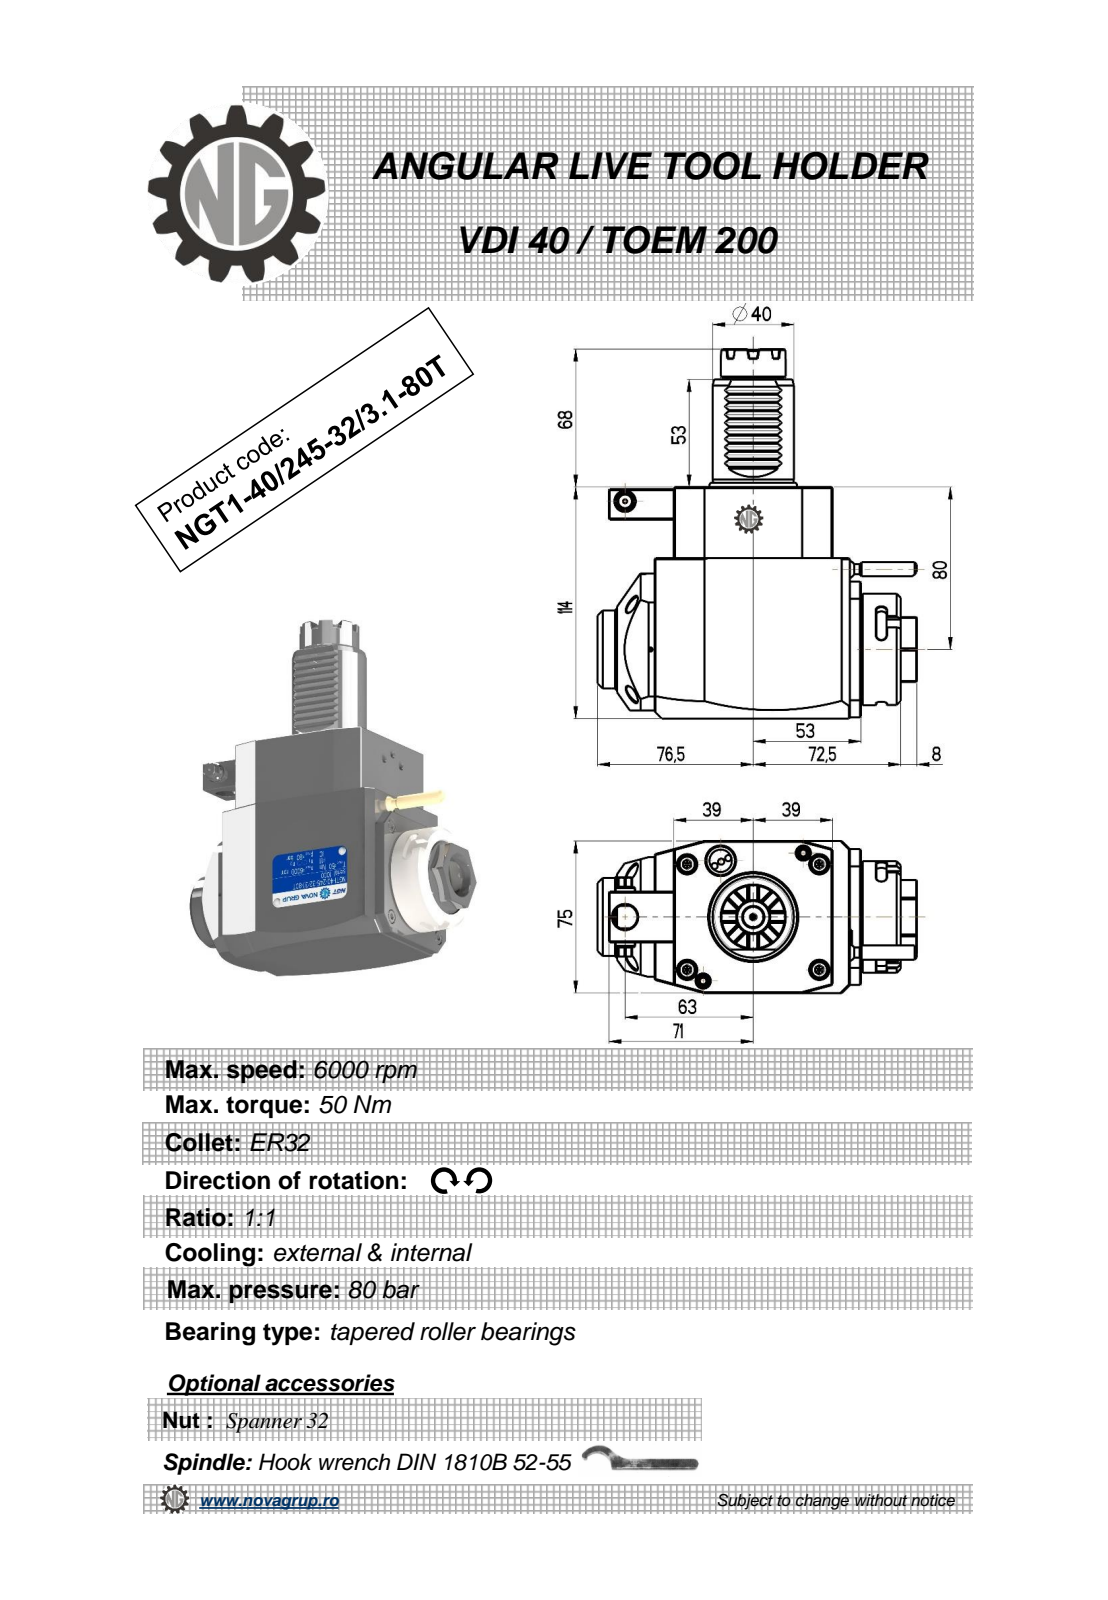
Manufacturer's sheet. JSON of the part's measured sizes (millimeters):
{"part_name": "NGT1_40_245_32_3_1_80T", "step_written_by": "PRO/ENGINEER BY PARAMETRIC TECHNOLOGY CORPORATION, 2010280 (CONFIG_CONTROL_DESIGN)", "units": "millimeters", "bodies": {"solids": 1, "faces": 430, "planar": 228, "cylindrical": 86, "other": 116}, "overall_size": [182, 157, 75], "volume_mm3": 972593, "surface_area_mm2": 73823, "round_holes": [[2, 1], [2.5, 1], [3, 1], [4.5, 1], [9.5, 1], [12, 1], [23, 1]], "round_bosses_or_shafts": [[8, 2], [55, 1], [48, 1], [40, 1], [38.5, 1], [32, 1], [17.2, 1], [10, 1]], "partial_cylinders_radius": [[0.3, 10], [2.5, 6], [180, 2], [0.5, 1], [3.85, 1], [4.25, 1], [24.5, 1], [37.5, 1]], "face_to_face_distances": [75, 114, 14, 78, 92, 25, 111.5, 33.5, 19.5, 35], "hole_center_spacings": [37.35, 43.2, 72.5]}
